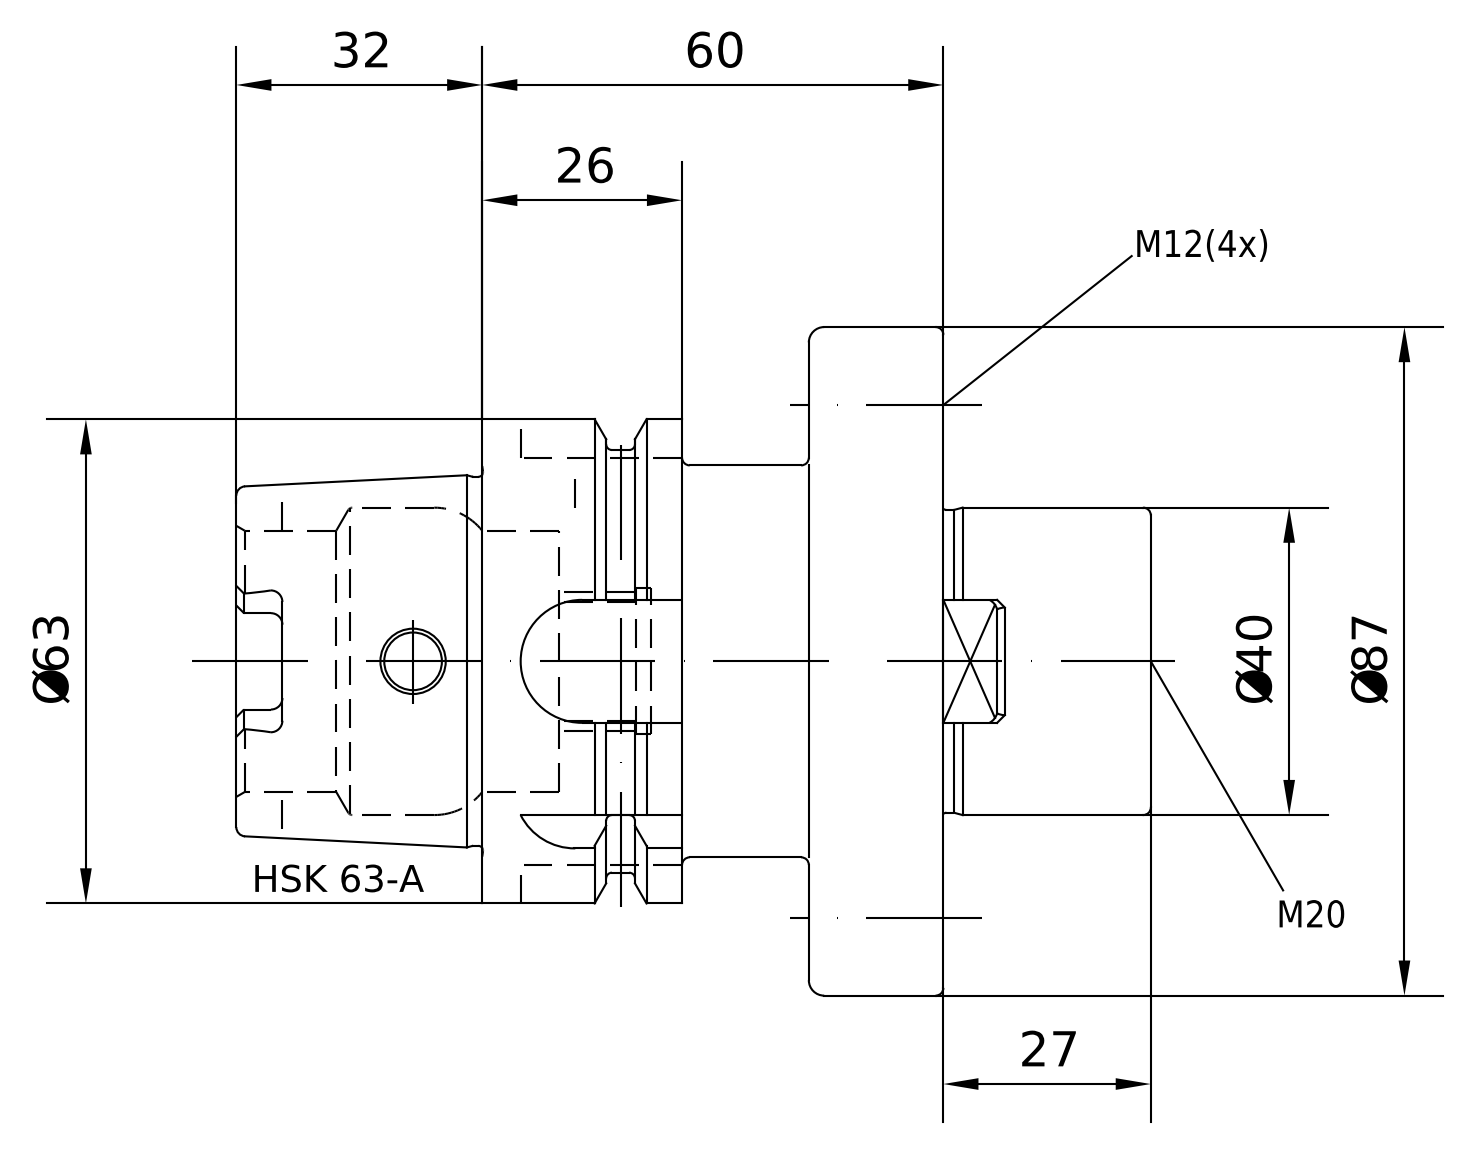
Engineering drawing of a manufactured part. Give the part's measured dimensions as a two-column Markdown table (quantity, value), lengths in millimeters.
| quantity | value |
| --- | --- |
| part name | A63-050-40 |
| STEP written by | PRO/ENGINEER BY PARAMETRIC TECHNOLOGY CORPORATION, 2010430 (CONFIG_CONTROL_DESIGN) |
| units | millimeters |
| bodies | 1 solid, 214 faces (70 planar, 70 cylindrical, 74 other) |
| overall size | 119 × 87 × 87 |
| volume | 240 263 mm³ |
| surface area | 50 627 mm² |
| round holes (diameter × count) | 10.2 × 4, 12 × 4, 7.5 × 1, 10 × 1, 16.92 × 1, 17.5 × 1, 18.32 × 1, 18.66 × 1, 20 × 1, 34 × 1, 40 × 1 |
| round bosses / shafts (diameter × count) | 87 × 1, 63 × 1, 55 × 1, 51 × 1, 48.04 × 1, 18 × 1 |
| partial cylindrical surfaces (radius × count) | 1.5 × 6, 3 × 4, 8 × 1, 8.02 × 1, 9.02 × 1 |
| main face-to-face distances | 17.5, 42.5, 60, 16, 27, 87, 44.5, 42, 58, 34 |
| hole center spacings | 33.35, 47.16, 66.69 |
